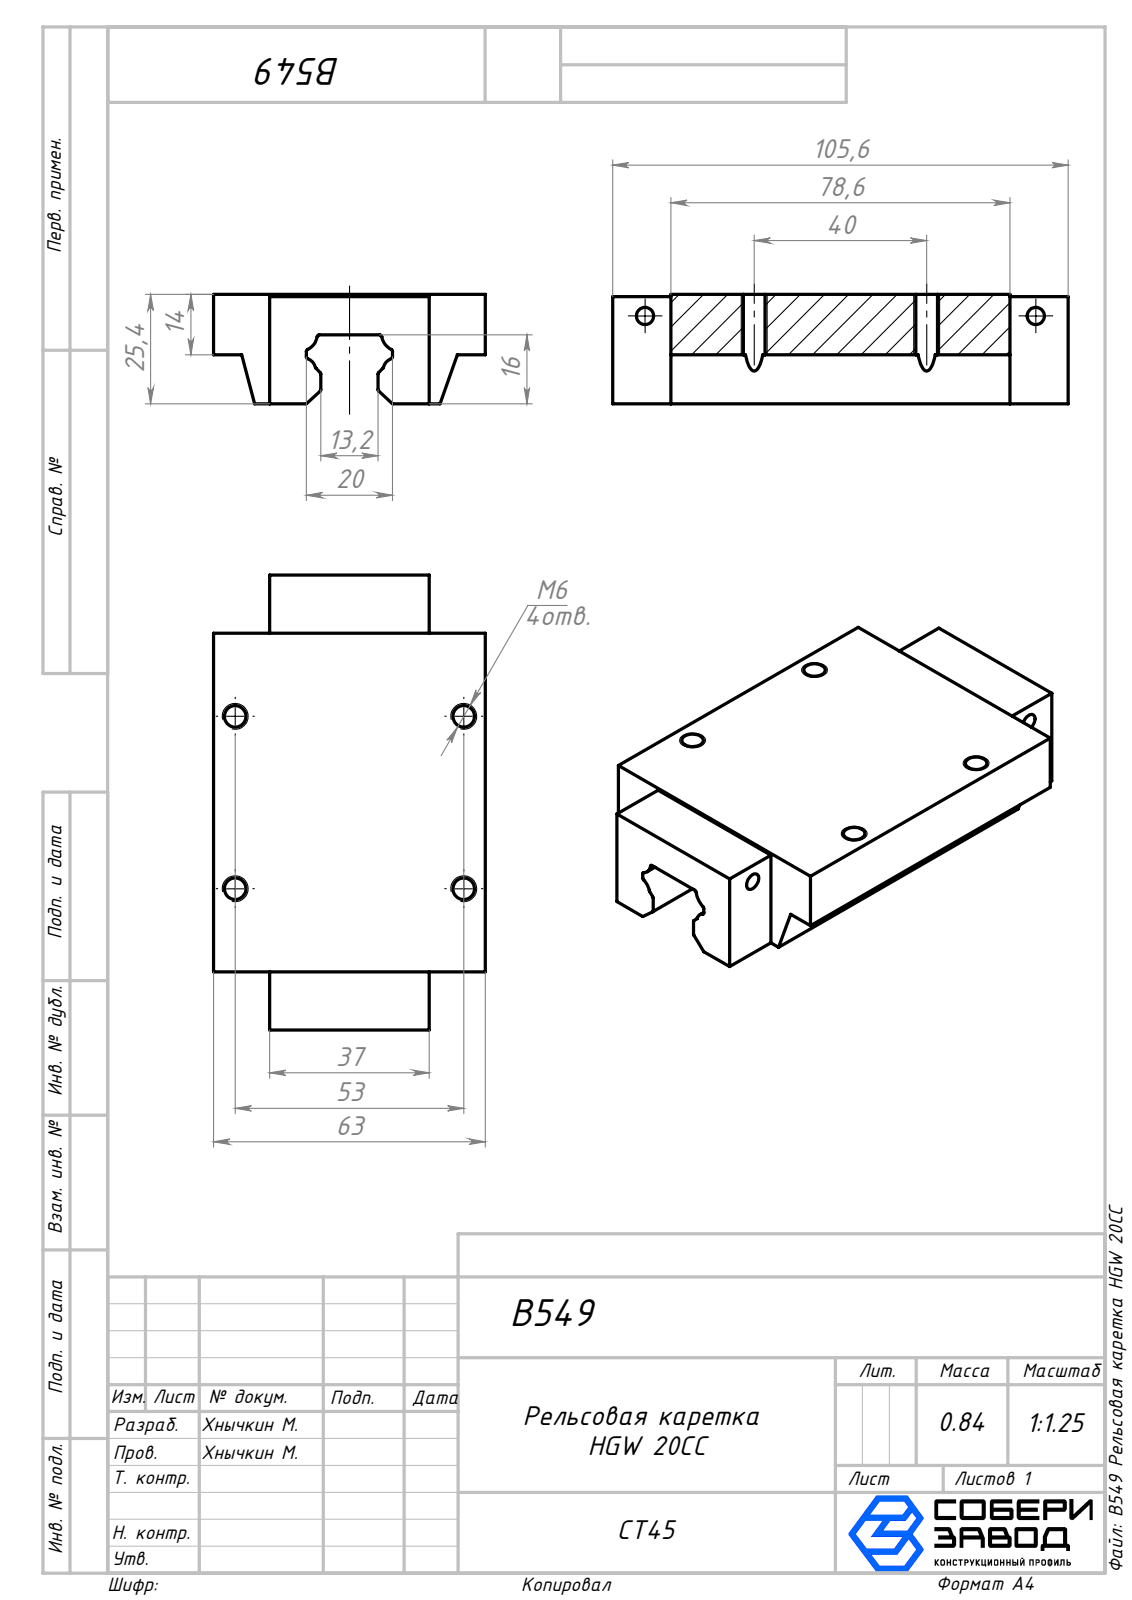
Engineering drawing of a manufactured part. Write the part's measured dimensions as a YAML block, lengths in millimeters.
part_name: "B549 Рельсовая каретка HGW 20CC"
step_written_by: "SolidWorks 2026 (AUTOMOTIVE_DESIGN)"
units: millimeters
bodies: {solids: 1, faces: 56, planar: 28, cylindrical: 28, other: 0}
overall_size: [105.6, 63, 25.4]
volume: 106770
surface_area: 24320
round_holes:
  - {diameter: 5, count: 4}
  - {diameter: 4, count: 2}
partial_cylinders:
  - {radius: 0.5, count: 12}
  - {radius: 3, count: 2}
  - {radius: 4, count: 2}
face_to_face_distances: [25.4, 13.5, 16, 9.4, 13, 50, 63, 24.9, 8.9, 0.5]
hole_center_spacings: [40, 53, 66.4, 90.6]
